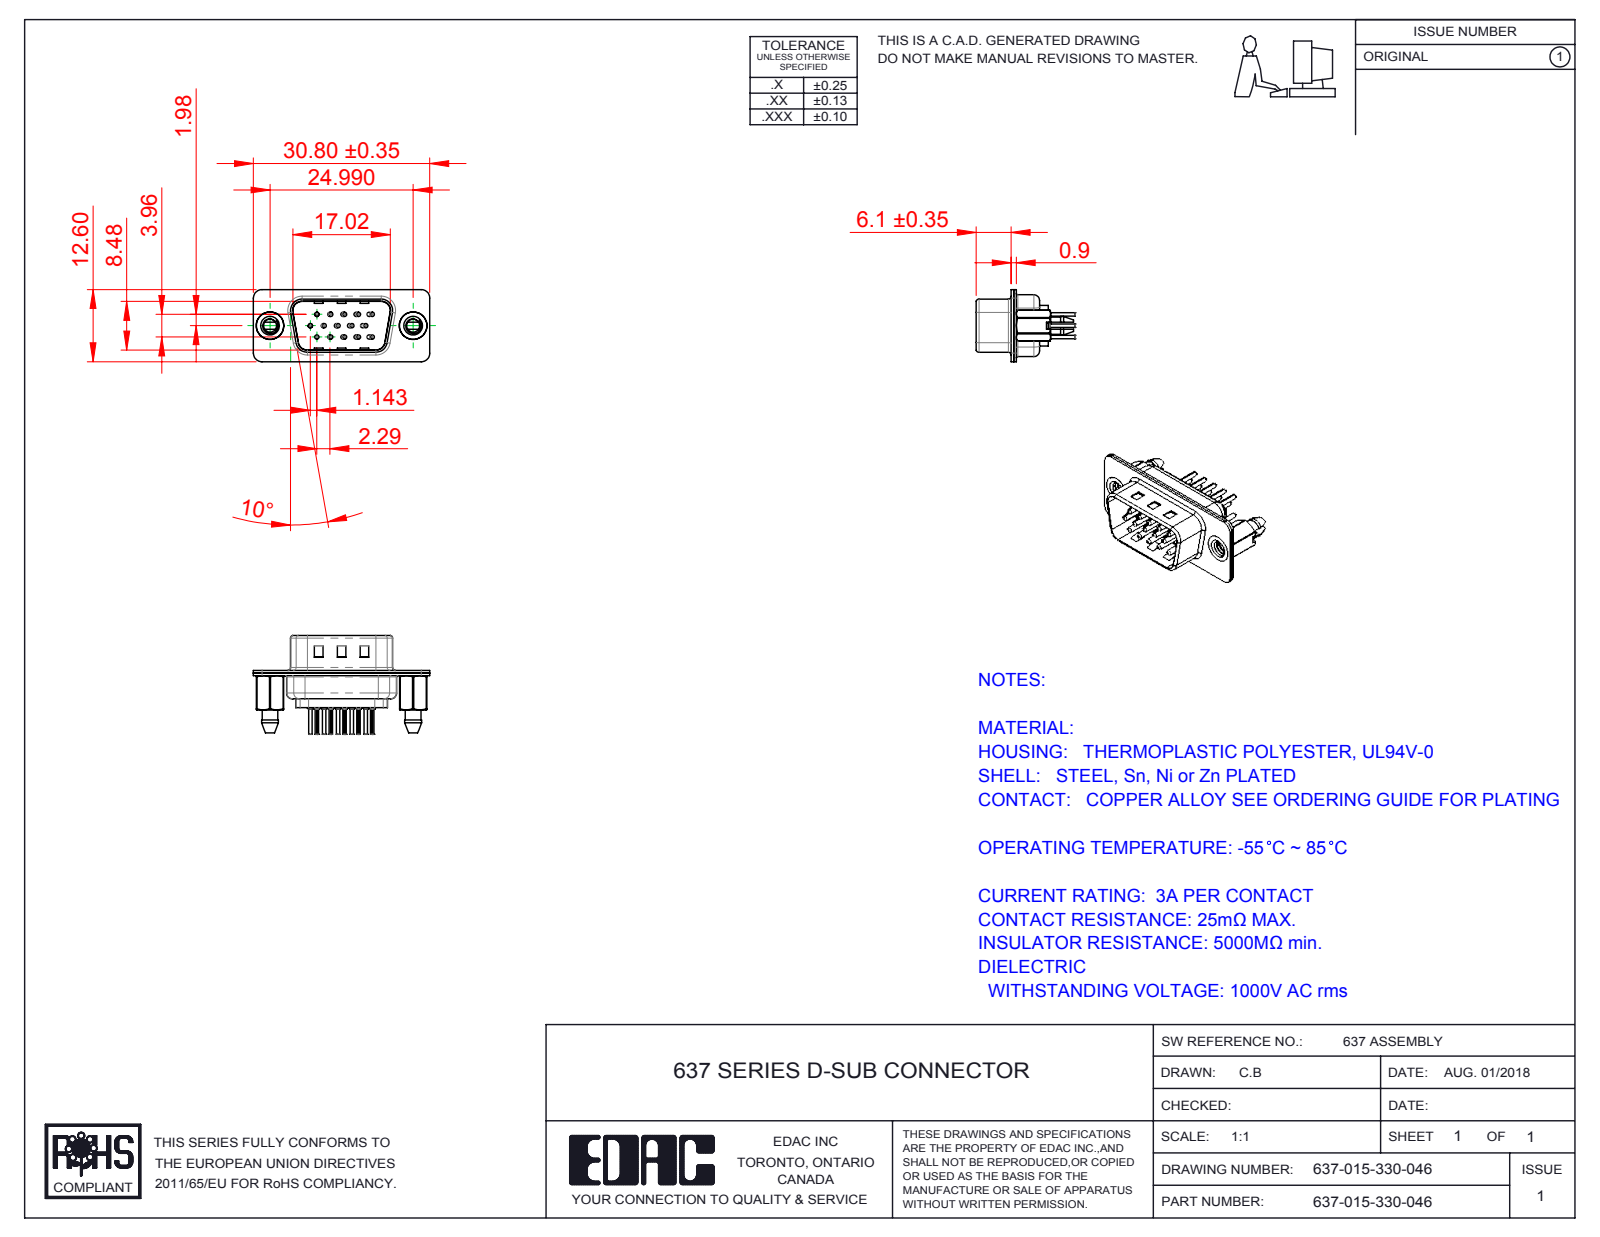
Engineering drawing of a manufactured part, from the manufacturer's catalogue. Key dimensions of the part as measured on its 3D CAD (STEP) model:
Part name (STEP PRODUCT): 637 Contact Row 3_30; 637 Contact Row 1_30; 637 Shell Rear_15 Contacts; 637 Shell Front_15 Contacts (+4 more)
STEP written by: SolidWorks 2016 (CONFIG_CONTROL_DESIGN)
Units: millimetres
Bodies: 20 solids, 1878 faces (499 planar, 716 cylindrical, 663 other)
Overall size (bounding box): 30.8 × 17.25 × 12.6
Volume: 1 429 mm³ · Surface area: 4 933 mm²
Round holes (diameter × count): ⌀1.6 ×27, ⌀0.2 ×15, ⌀0.35 ×15, ⌀1.1 ×15, ⌀0.75 ×12, ⌀2 ×12, ⌀2.26 ×2, ⌀4 ×2, ⌀4.8 ×2
Round bosses / shafts (diameter × count): ⌀2 ×15, ⌀1.5 ×15, ⌀0.75 ×15, ⌀0.6 ×15, ⌀4.9 ×2
Partial cylindrical surfaces — rounded edges, fillets, slot ends (radius × count): R0.1 ×30, R1.5 ×18, R2 ×12, R0.5 ×8, R1.6 ×6, R0.25 ×4, R0.55 ×4, R0.7 ×4
Main face-to-face distances: 0.45, 0.4, 0.9, 8.48, 0.7, 8.88, 6.5, 4.55, 0.31, 1.05
Hole centre spacings: 3.96, 2.29, 2.28, 4.57, 2.42, 6.05, 4.84, 2.35
